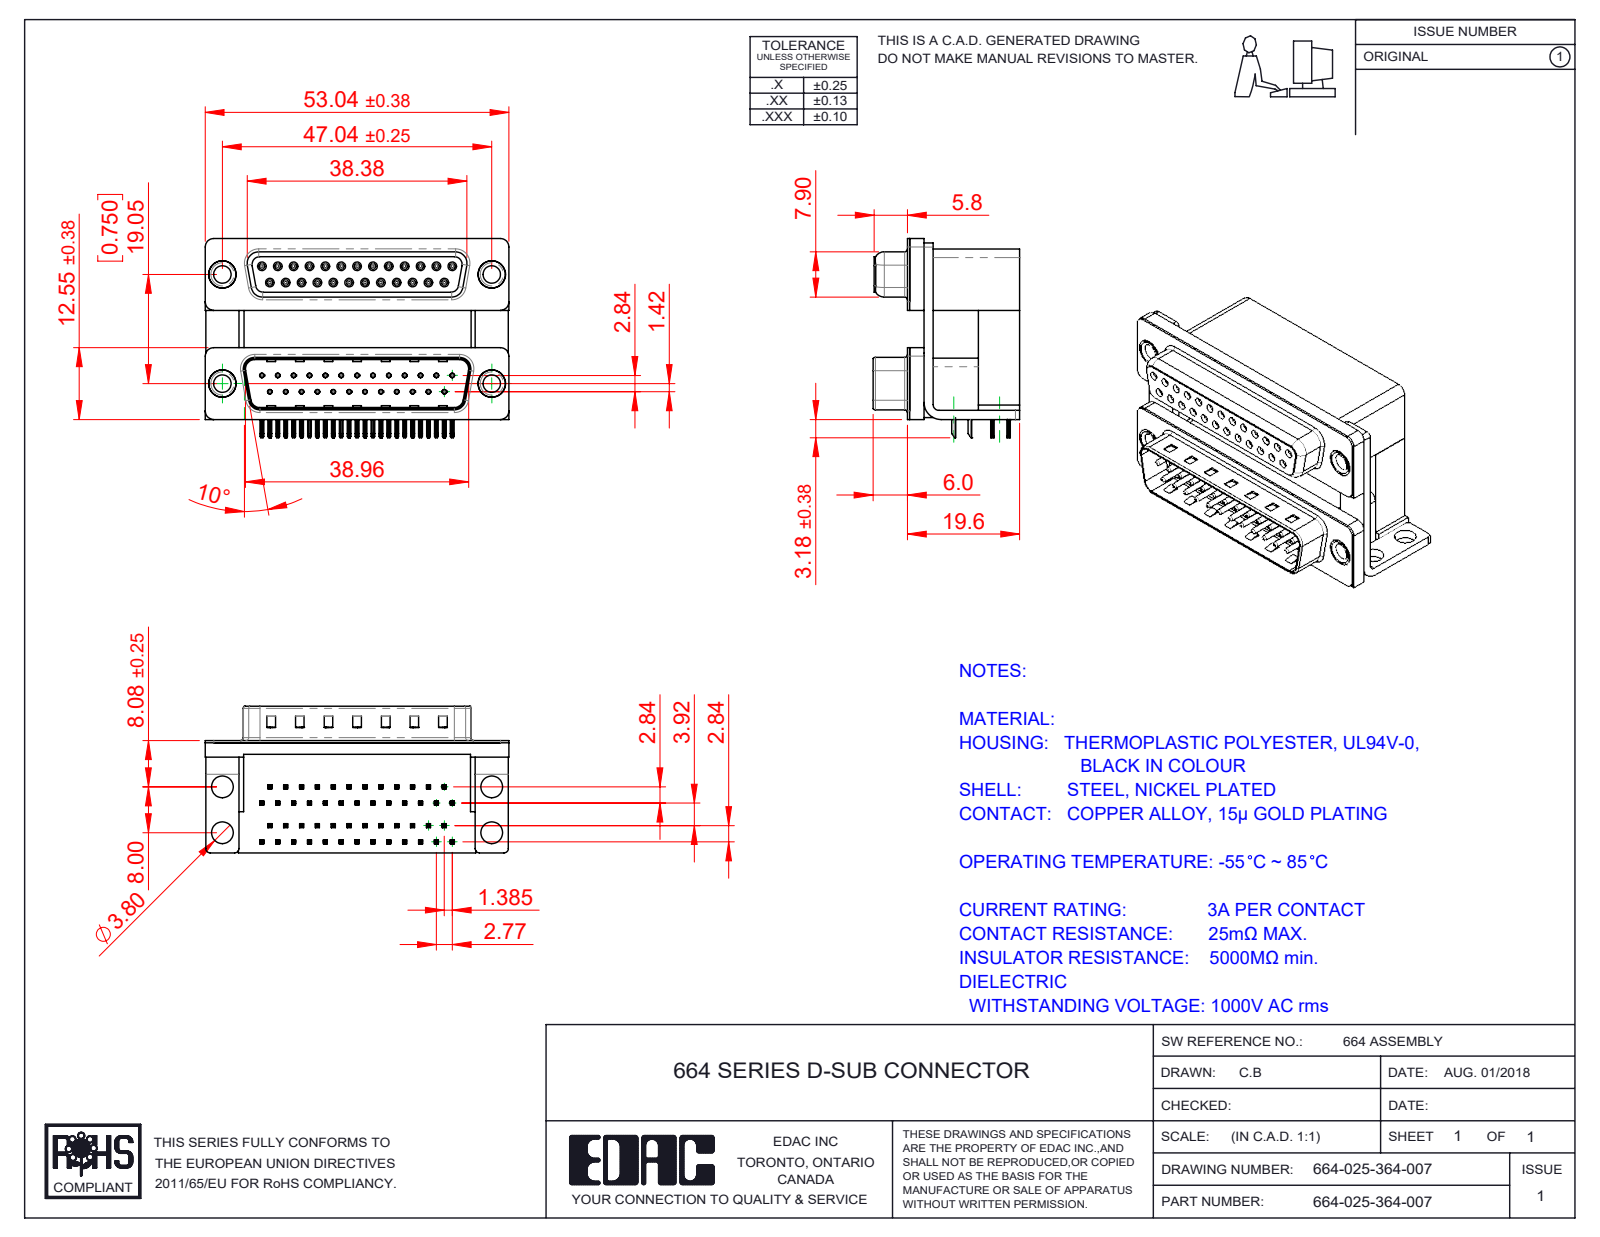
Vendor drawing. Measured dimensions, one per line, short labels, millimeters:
name: 664 Housing Lower_25 Contacts; 664 Contact Top Lower; 664 Thru Hole Rivet; 664 Contact Bottom Lower (+8 more)
written by: SolidWorks 2020 (CONFIG_CONTROL_DESIGN)
unit: mm
bodies: 61 solids, 6119 faces (3257 planar, 1507 cylindrical, 1355 other)
size: 53.04 × 34.78 × 25.6
volume: 22 444 mm³; area: 23 971 mm²
holes: 50× ⌀0.8, 25× ⌀0.35, 25× ⌀0.9, 4× ⌀3.05, 4× ⌀3.5, 4× ⌀3.8, 4× ⌀4, 4× ⌀4.8, 4× ⌀5
bosses: 25× ⌀1.2, 25× ⌀0.75, 4× ⌀4.9, 4× ⌀4.75, 4× ⌀3.85
rounds: 200× R0.1, 100× R0.15, 100× R0.25, 50× R0.12, 50× R0.35, 25× R0.34, 14× R1.5, 12× R0.28
face distances: 0.4, 19.2, 7.2, 12, 10.69, 16.7, 9.5, 2.5, 2.84, 18.71
hole spacings: 2.77, 3.16, 5.54, 8.31, 11.08, 13.85, 16.62, 5.03
